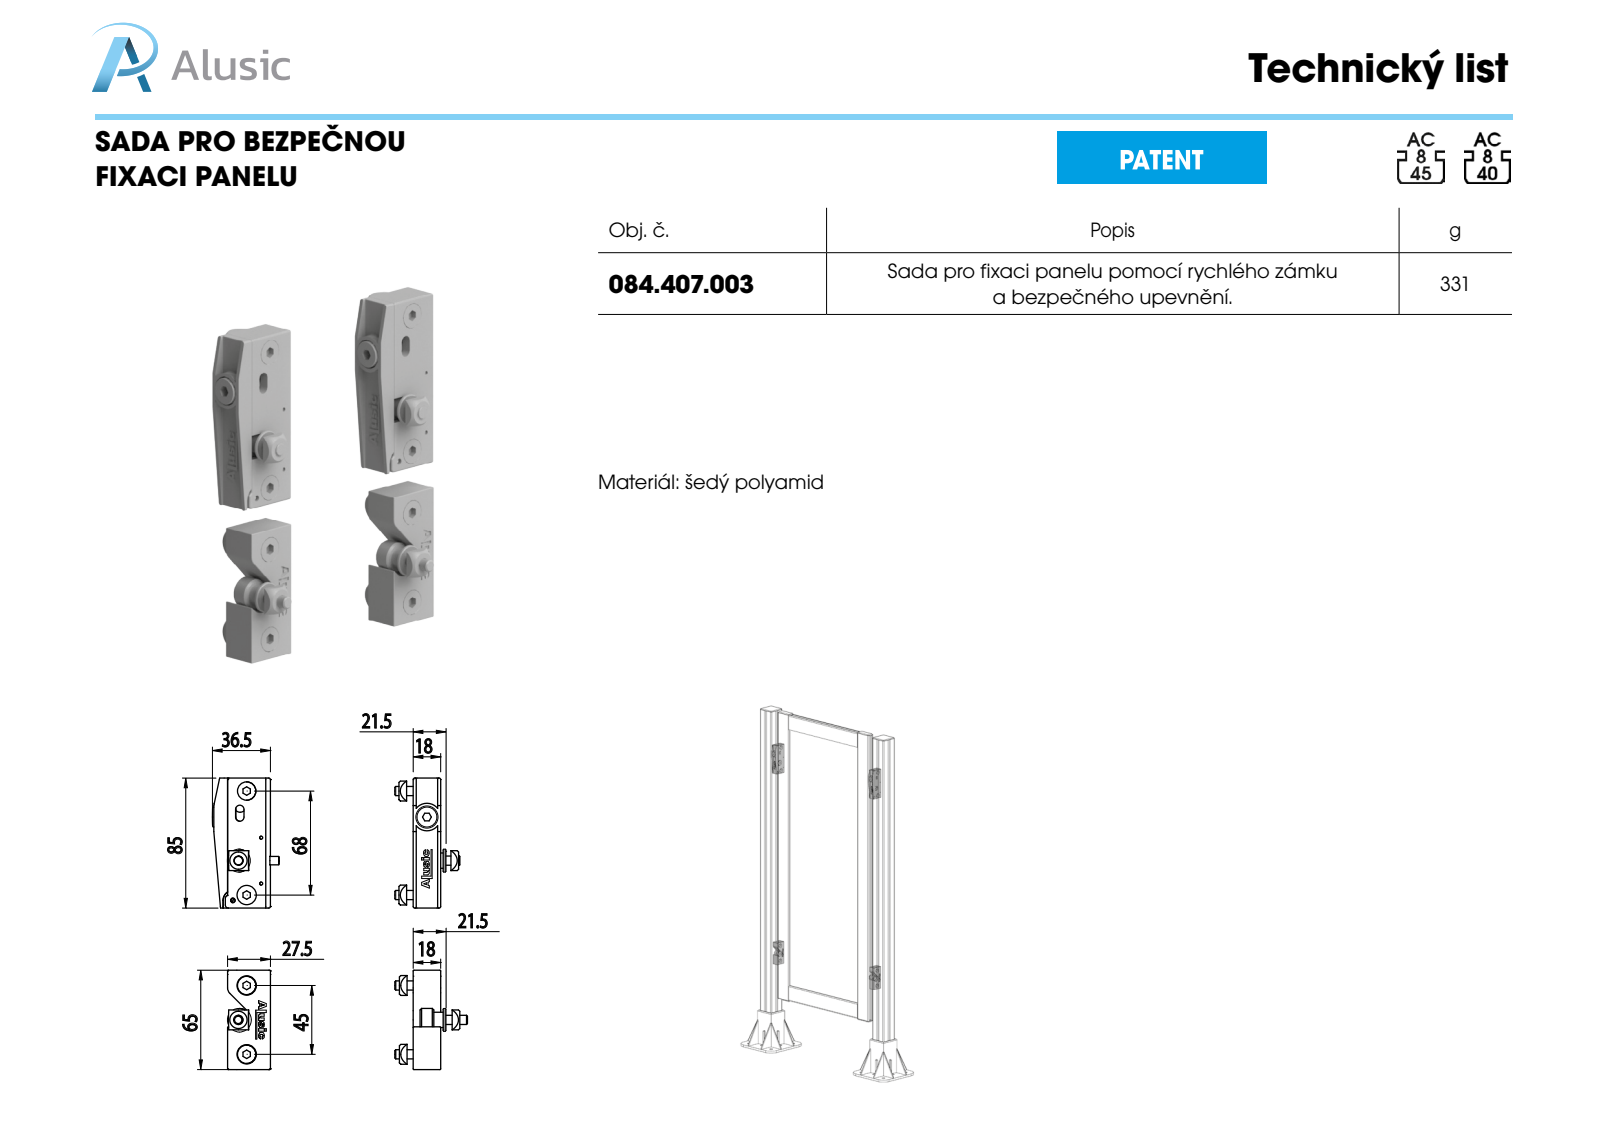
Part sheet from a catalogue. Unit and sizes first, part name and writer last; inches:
Units: inches
Overall size (bounding box): 8.557 × 6.395 × 1.703
Round holes (diameter × count): ⌀0.236 ×8, ⌀0.26 ×6, ⌀0.079 ×2, ⌀0.197 ×2, ⌀0.335 ×2, ⌀0.413 ×2, ⌀0.571 ×2, ⌀0.118 ×1, ⌀0.126 ×1, ⌀0.217 ×1
Round bosses / shafts (diameter × count): ⌀0.472 ×4, ⌀0.138 ×4, ⌀0.591 ×2, ⌀0.512 ×2, ⌀0.394 ×2, ⌀0.315 ×2, ⌀0.217 ×2, ⌀0.197 ×2
Partial cylindrical surfaces — rounded edges, fillets, slot ends (radius × count): R0.02 ×43, R0.039 ×34, R0.01 ×8, R0.012 ×8, R0.022 ×8, R0.028 ×8, R0.053 ×8, R0.088 ×8
Main face-to-face distances: 6.904, 0.709, 0.236, 1.083, 0.098, 0.984, 6.195, 0.472, 7.613, 0.157
Hole centre spacings: 0.907, 2.677, 1.122, 2.113, 2.989, 6.904, 0.821, 1.218
Volume: 9.504 in³ · Surface area: 134.6 in²
Bodies: 52 solids, 1708 faces (752 planar, 672 cylindrical, 284 other)
Part name (STEP PRODUCT): 084.407.003; VITI TSEI UNI 5933_M6x30 UNI 5933; VITI TCEI UNI 5931_M6x25 UNI 5931; 084.407.105 (+8 more)
STEP written by: SolidWorks 2016 (AUTOMOTIVE_DESIGN)
